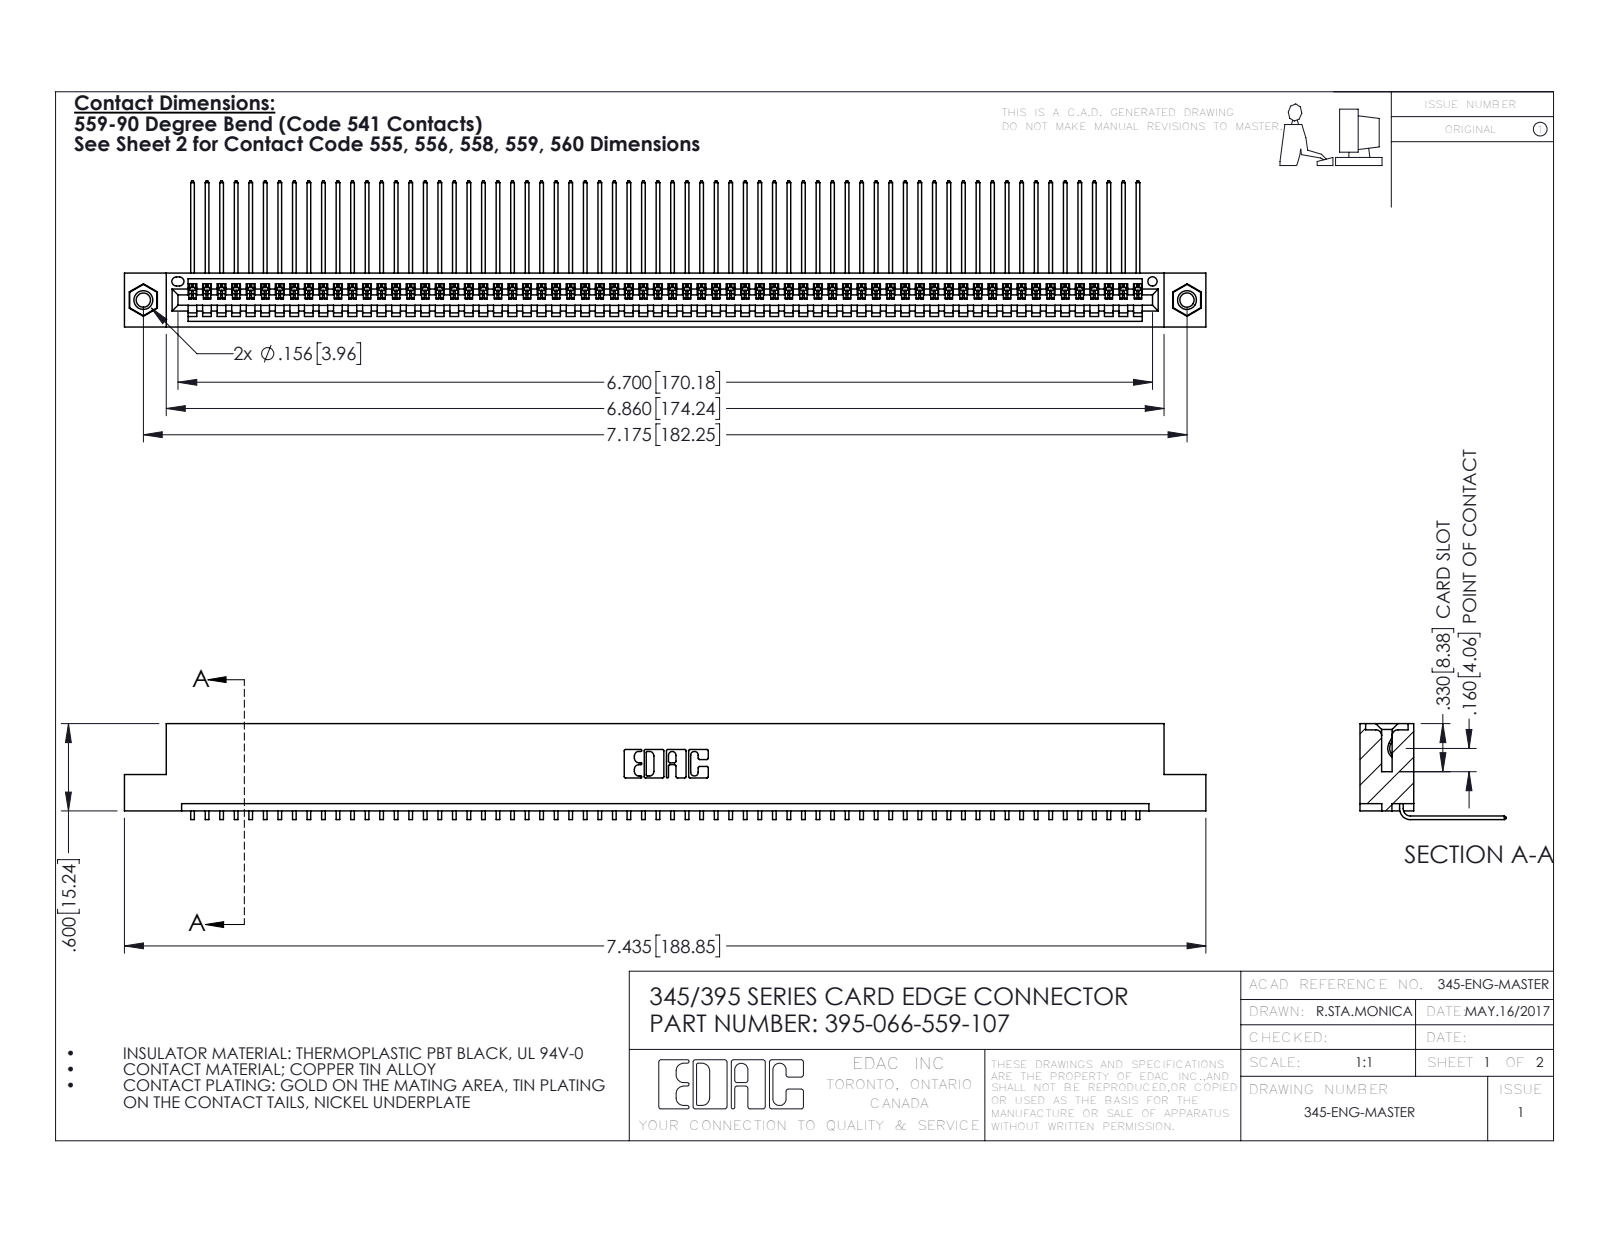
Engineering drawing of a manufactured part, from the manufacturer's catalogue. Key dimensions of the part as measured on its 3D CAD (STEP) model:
Part name (STEP PRODUCT): 395-066-559-107; 345-250-001_345-250-005-103; 345 Part_Flush Mounting Lugs - 0.156 Dia-TI; 345-292-001_558 559 Tail - 1
STEP written by: SolidWorks 2016 (CONFIG_CONTROL_DESIGN)
Units: inches
Bodies: 69 solids, 4146 faces (2884 planar, 1246 cylindrical, 16 other)
Overall size (bounding box): 7.435 × 1.005 × 0.659
Volume: 1.119 in³ · Surface area: 40.34 in²
Round holes (diameter × count): ⌀0.098 ×2, ⌀0.125 ×2, ⌀0.156 ×2, ⌀0.064 ×1
Round bosses / shafts (diameter × count): ⌀0.155 ×2
Partial cylindrical surfaces — rounded edges, fillets, slot ends (radius × count): R0.006 ×132, R0.01 ×22, R0.007 ×6, R0.031 ×6, R0.026 ×3, R0.031 ×2, R0.04 ×2, R0.014 ×1
Main face-to-face distances: 0.072, 0.298, 0.37, 0.2, 0.098, 0.272, 0.025, 0.225, 0.149, 0.072
Hole centre spacings: 0.27, 6.939, 7.175
